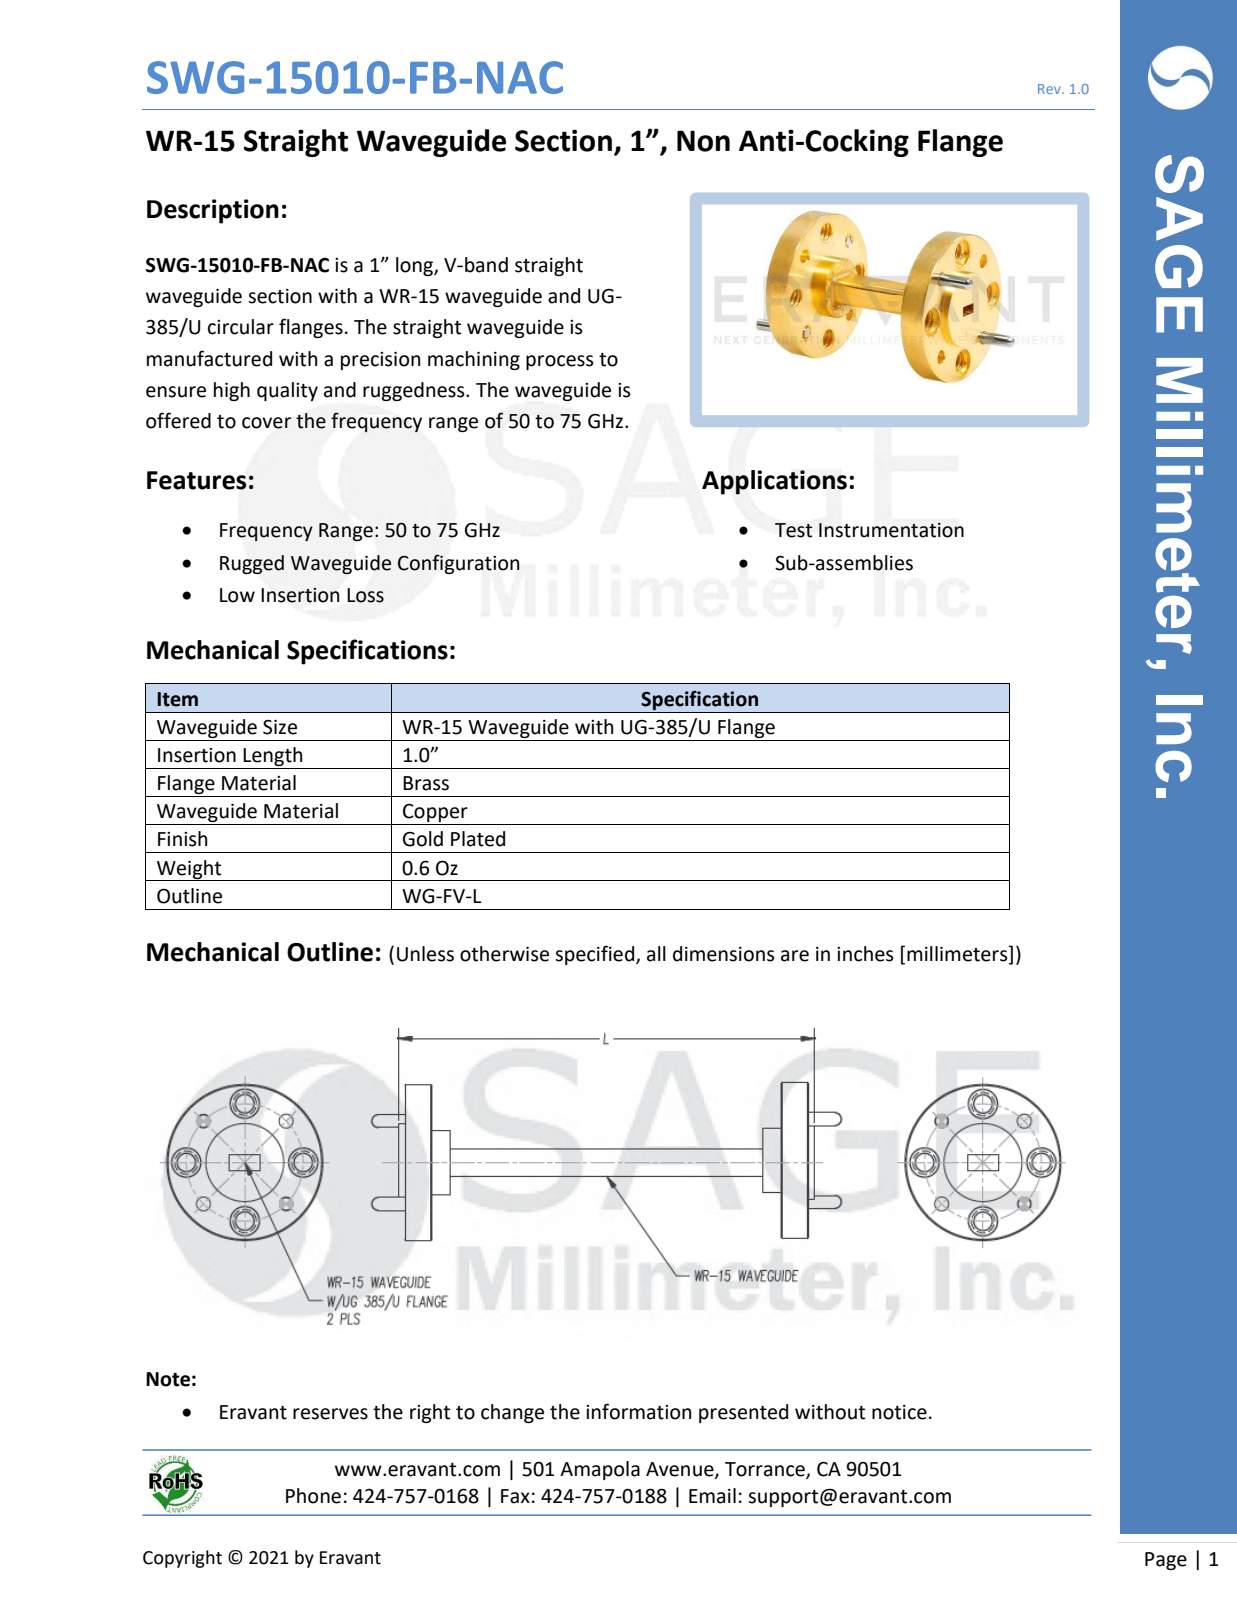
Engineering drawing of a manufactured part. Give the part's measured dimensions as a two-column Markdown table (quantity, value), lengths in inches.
| quantity | value |
| --- | --- |
| part name | SWG-15010-FB |
| STEP written by | SolidWorks 2013 (CONFIG_CONTROL_DESIGN) |
| units | inches |
| bodies | 5 solids, 140 faces (32 planar, 68 cylindrical, 40 other) |
| overall size | 1.305 × 0.75 × 0.75 |
| volume | 0.138 in³ |
| surface area | 3.966 in² |
| round holes (diameter × count) | 0.061 × 4, 0.067 × 4, 0.089 × 4, 0.14 × 4 |
| round bosses / shafts (diameter × count) | 0.063 × 4, 0.75 × 1, 0.375 × 1, 0.36 × 1 |
| main face-to-face distances | 0.13, 0.81, 0.04, 0.68, 0.94, 0.114, 0.03, 0.16, 0.84, 0.97 |
| hole center spacings | 0.215, 0.398, 0.519, 0.562 |
